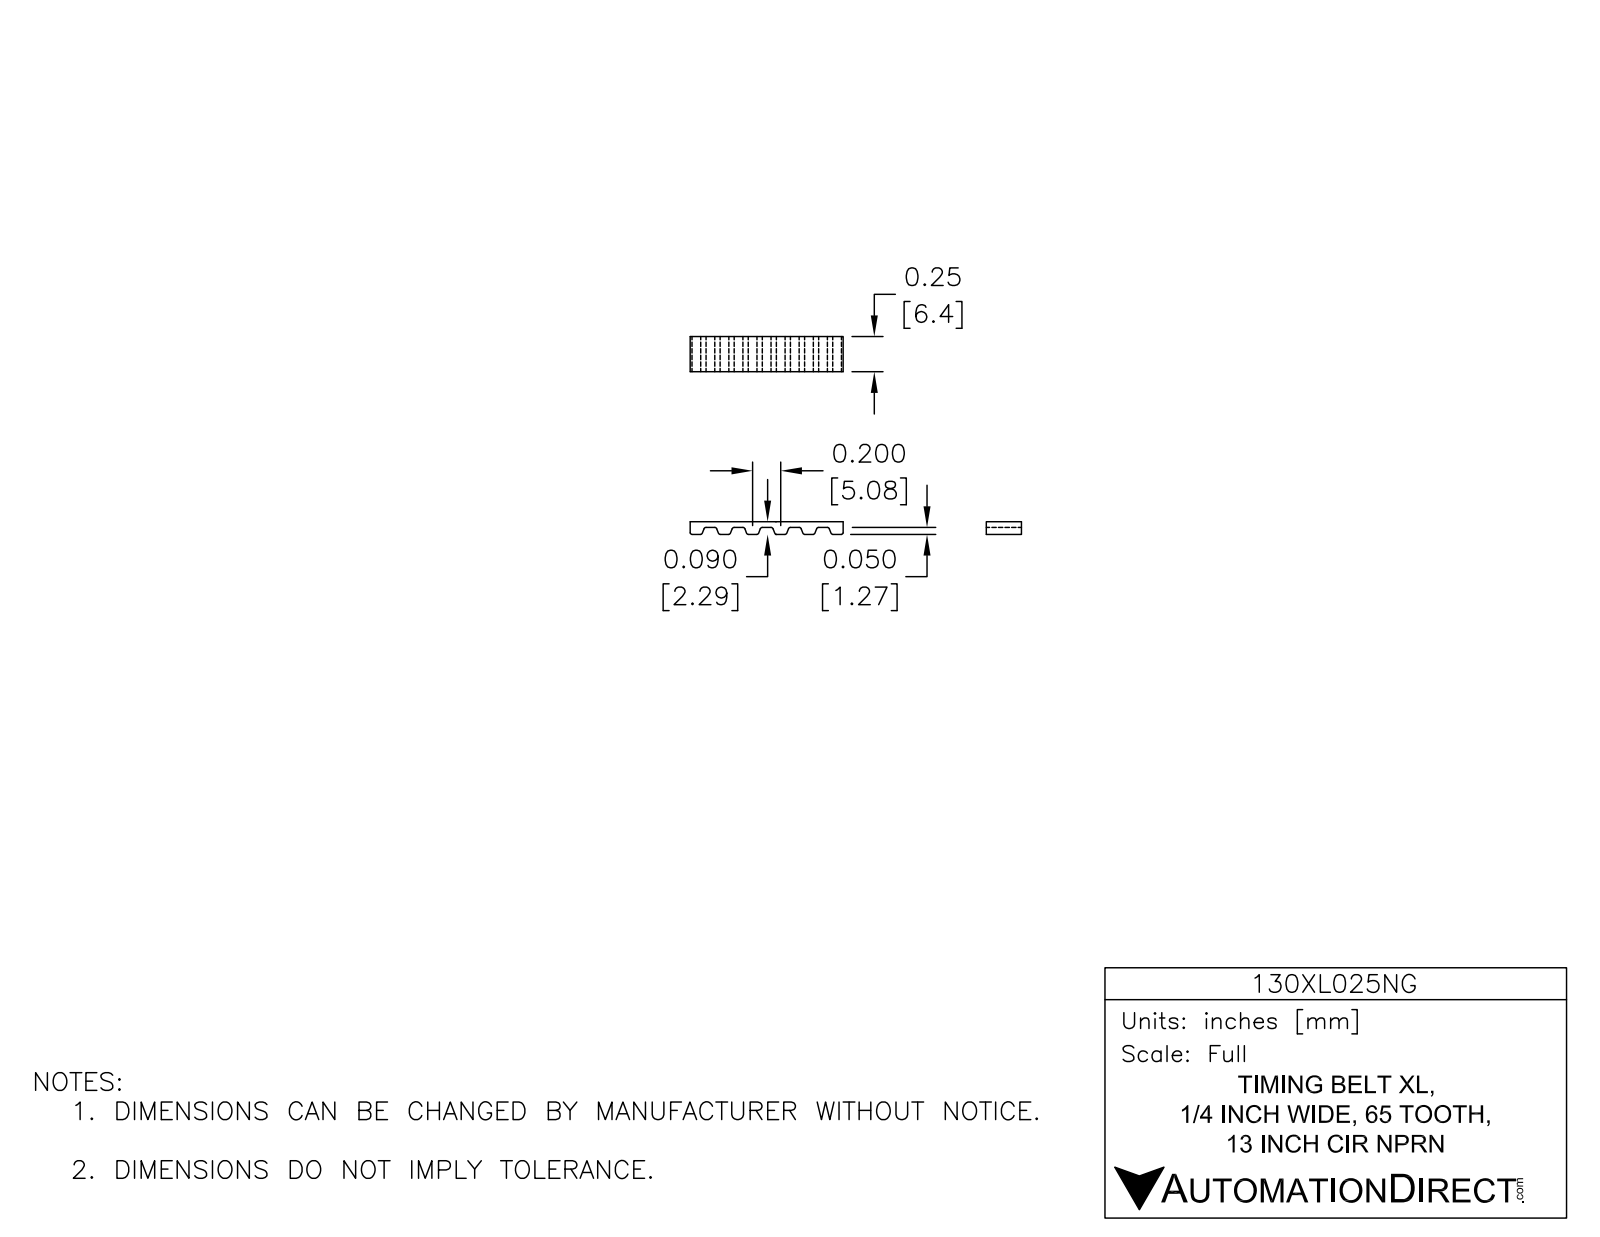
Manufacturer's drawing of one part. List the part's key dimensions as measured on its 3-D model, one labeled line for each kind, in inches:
Part name (STEP PRODUCT): 130XL025NG
STEP written by: SolidWorks 2014 (AUTOMOTIVE_DESIGN)
Units: inches
Bodies: 1 solid, 558 faces (218 planar, 340 cylindrical, 0 other)
Overall size (bounding box): 4.788 × 3 × 0.25
Volume: 0.176 in³ · Surface area: 8.743 in²
Partial cylindrical surfaces — rounded edges, fillets, slot ends (radius × count): R0.015 ×260, R1.46 ×2, R1.5 ×2
Main face-to-face distances: 0.25, 3, 0.04, 2.96, 0.533, 2.92, 0.178, 0.356, 1.072, 0.711
